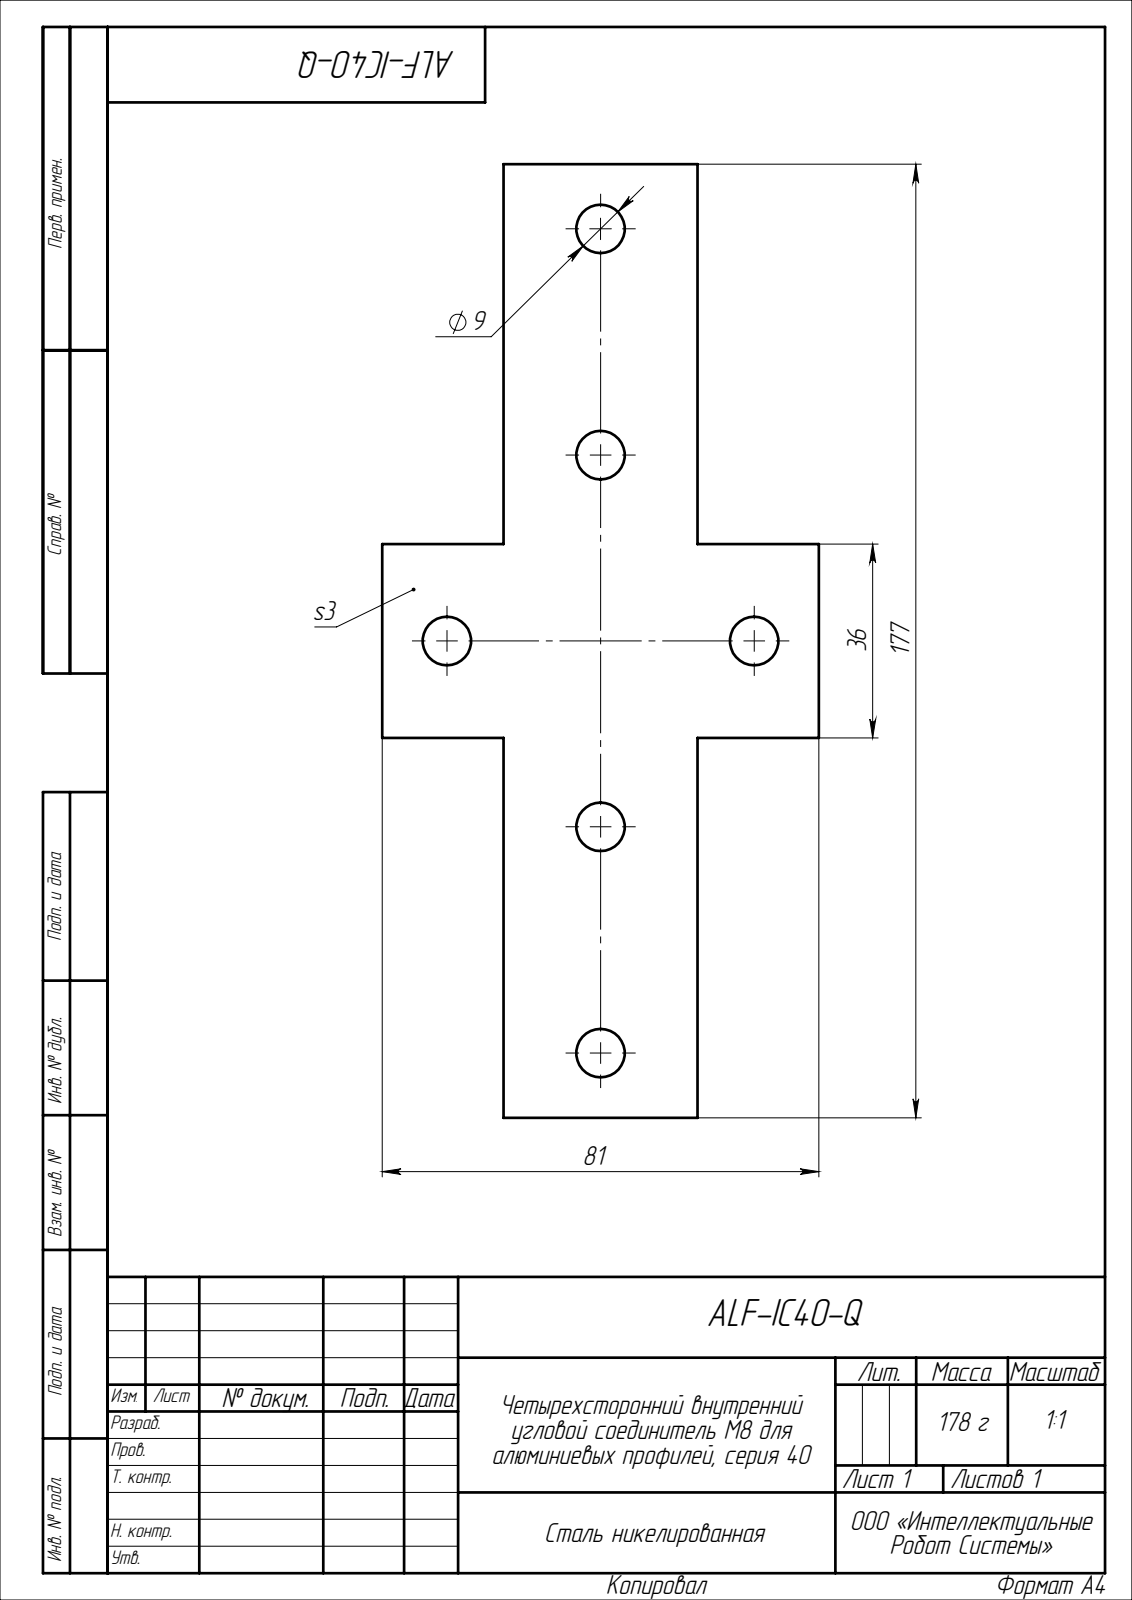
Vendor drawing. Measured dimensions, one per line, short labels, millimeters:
name: ALF-IC40-Q
written by: SolidWorks 2022 (CONFIG_CONTROL_DESIGN)
unit: mm
bodies: 1 solid, 26 faces (14 planar, 12 cylindrical, 0 other)
size: 177 × 81 × 3
volume: 22 831 mm³; area: 17 278 mm²
holes: 6× ⌀9
face distances: 3, 36, 22.5, 58.5, 70.5, 106.5, 81, 177
hole spacings: 44.75, 81.64, 42, 111, 57, 69, 153
